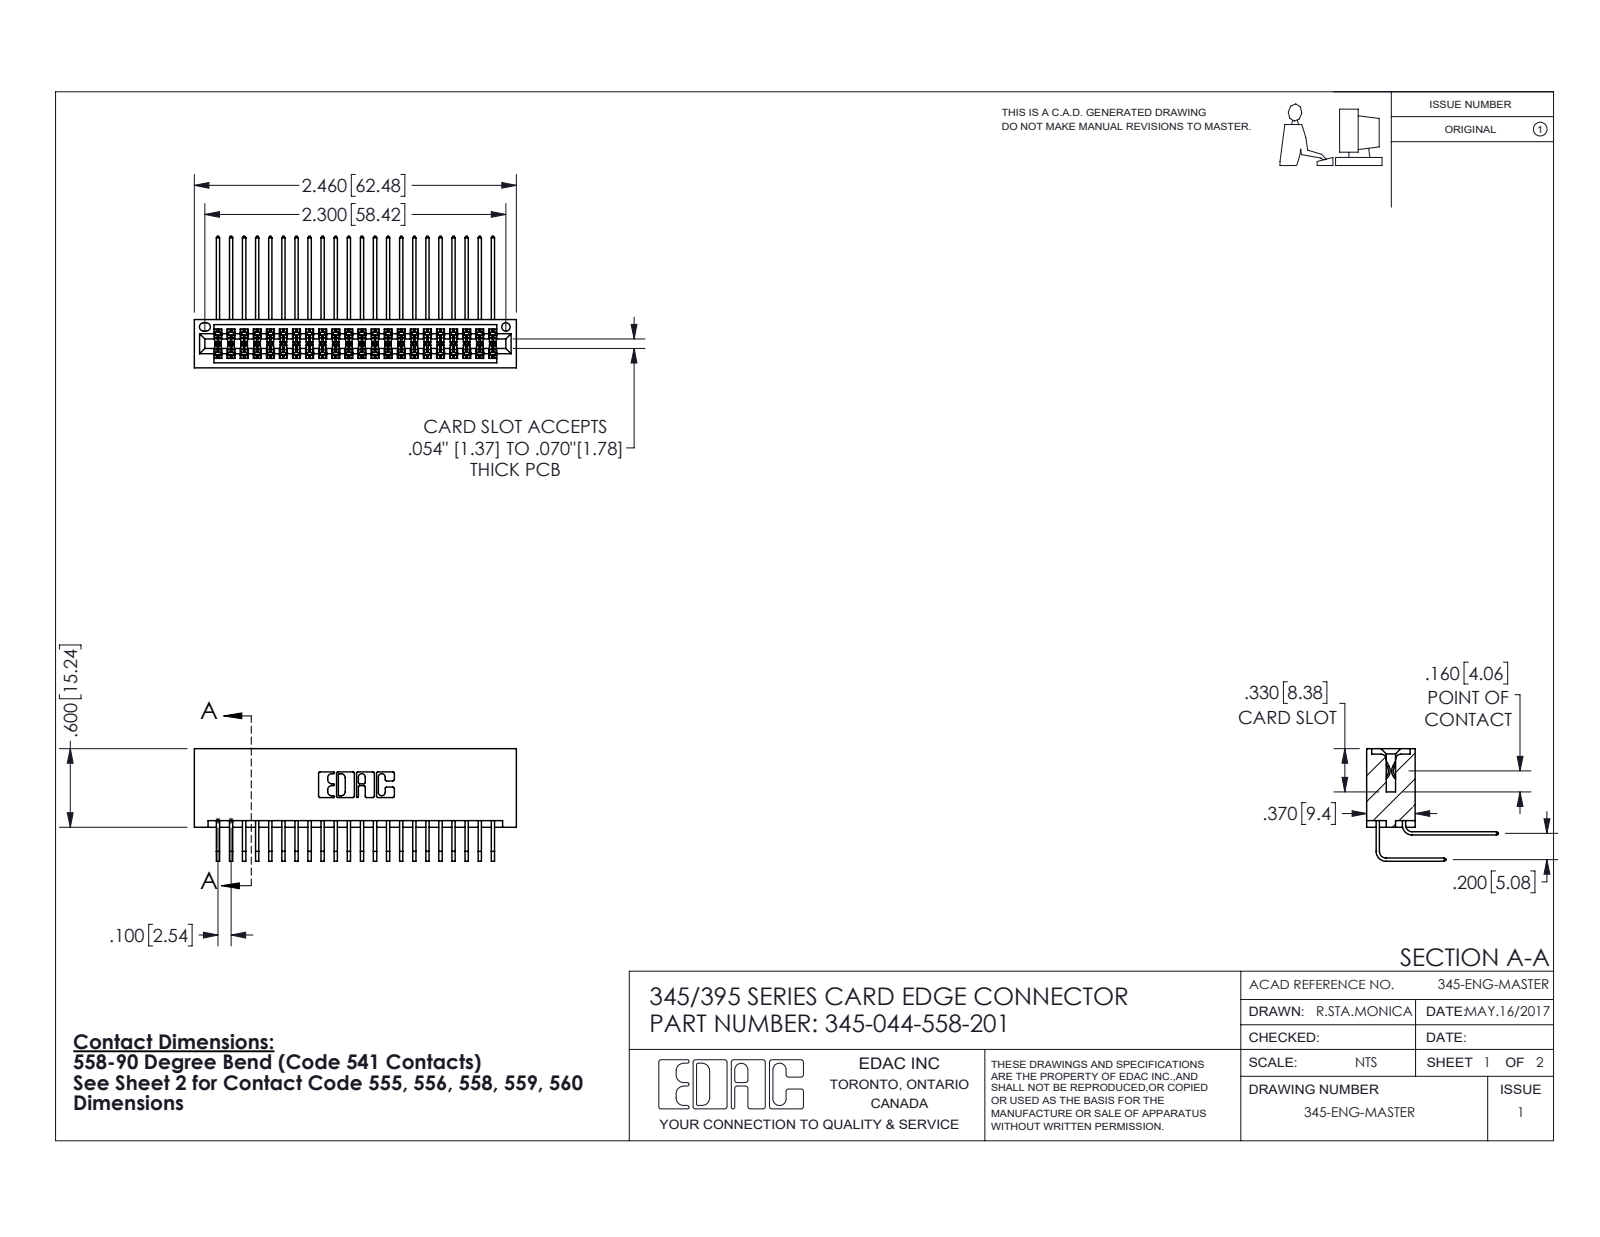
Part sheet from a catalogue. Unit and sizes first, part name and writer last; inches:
Units: inches
Overall size (bounding box): 2.46 × 1.005 × 0.859
Round holes (diameter × count): ⌀0.064 ×1
Partial cylindrical surfaces — rounded edges, fillets, slot ends (radius × count): R0.006 ×88, R0.01 ×22, R0.007 ×6, R0.031 ×6, R0.026 ×3, R0.014 ×2, R0.019 ×2, R0.022 ×2
Main face-to-face distances: 0.2, 0.072, 0.298, 0.37, 0.098, 0.272, 0.025, 0.225, 0.025, 0.175
Volume: 0.412 in³ · Surface area: 17.19 in²
Bodies: 45 solids, 2406 faces (1616 planar, 790 cylindrical, 0 other)
Part name (STEP PRODUCT): 345-292-001_558 559 Tail - 1; 345-044-558-201; 345 Part_No Mounting Lugs; 345-292-001_558 Tail - 2
STEP written by: SolidWorks 2016 (CONFIG_CONTROL_DESIGN)
